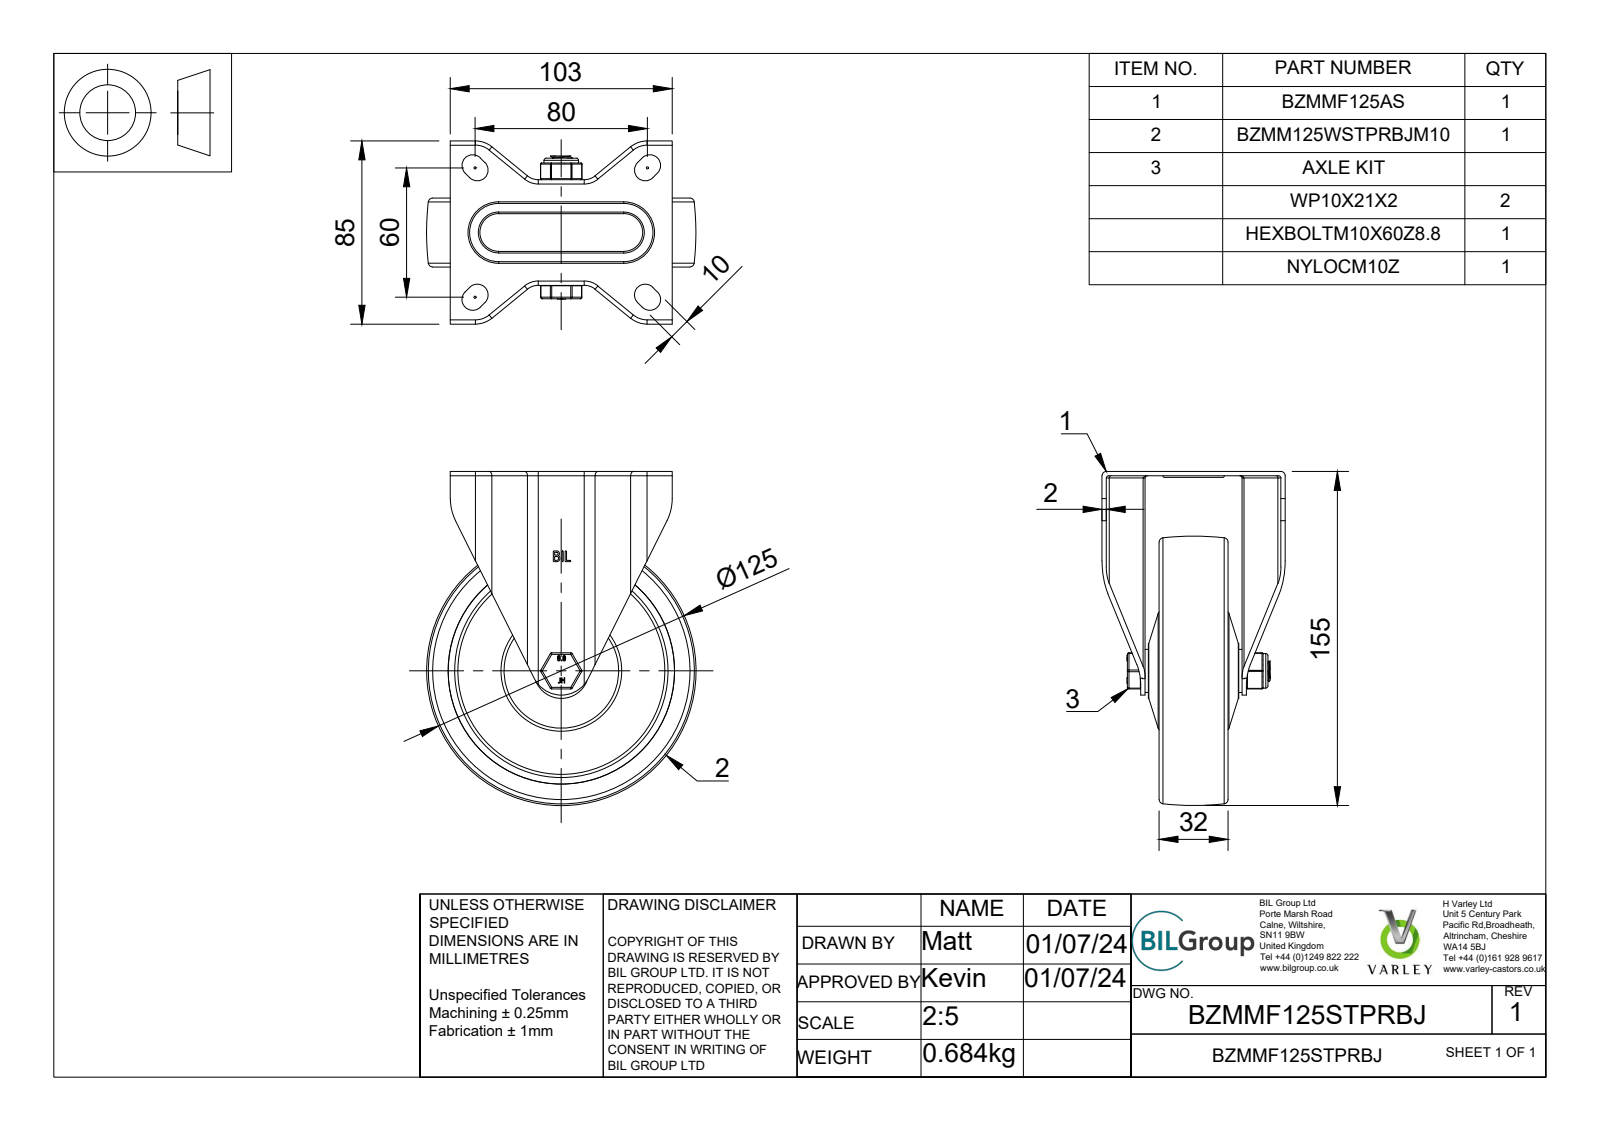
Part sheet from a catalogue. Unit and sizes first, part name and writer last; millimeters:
Units: millimetres
Overall size (bounding box): 155 × 125 × 85
Round holes (diameter × count): ⌀10 ×1, ⌀10.2 ×1, ⌀10.4 ×1, ⌀10.75 ×1, ⌀12 ×1, ⌀22.5 ×1, ⌀30 ×1, ⌀31 ×1, ⌀32 ×1, ⌀32.5 ×1, ⌀35 ×1, ⌀36.5 ×1
Round bosses / shafts (diameter × count): ⌀56 ×1, ⌀44.5 ×1, ⌀39 ×1, ⌀34.5 ×1, ⌀30.5 ×1, ⌀25.5 ×1, ⌀23 ×1, ⌀20 ×1
Partial cylindrical surfaces — rounded edges, fillets, slot ends (radius × count): R0.75 ×20, R0.5 ×18, R1 ×8, R2 ×8, R5 ×8, R12 ×5, R4 ×4, R6 ×4
Main face-to-face distances: 2, 13.75, 18.25, 18.84, 4.5, 6.5, 20.25, 24.75, 38.5, 40.5
Volume: 260 503 mm³ · Surface area: 150 644 mm²
Bodies: 23 solids, 787 faces (288 planar, 211 cylindrical, 288 other)
Part name (STEP PRODUCT): BZMMF125STPRBJ v4; BZMMF125AS v1; BZMMF125AS; ZINC PLATED, PRESSED STEEL BRACKET (+7 more)
STEP written by: Autodesk Translation Framework v13.14.0.145 (AUTOMOTIVE_DESIGN)
